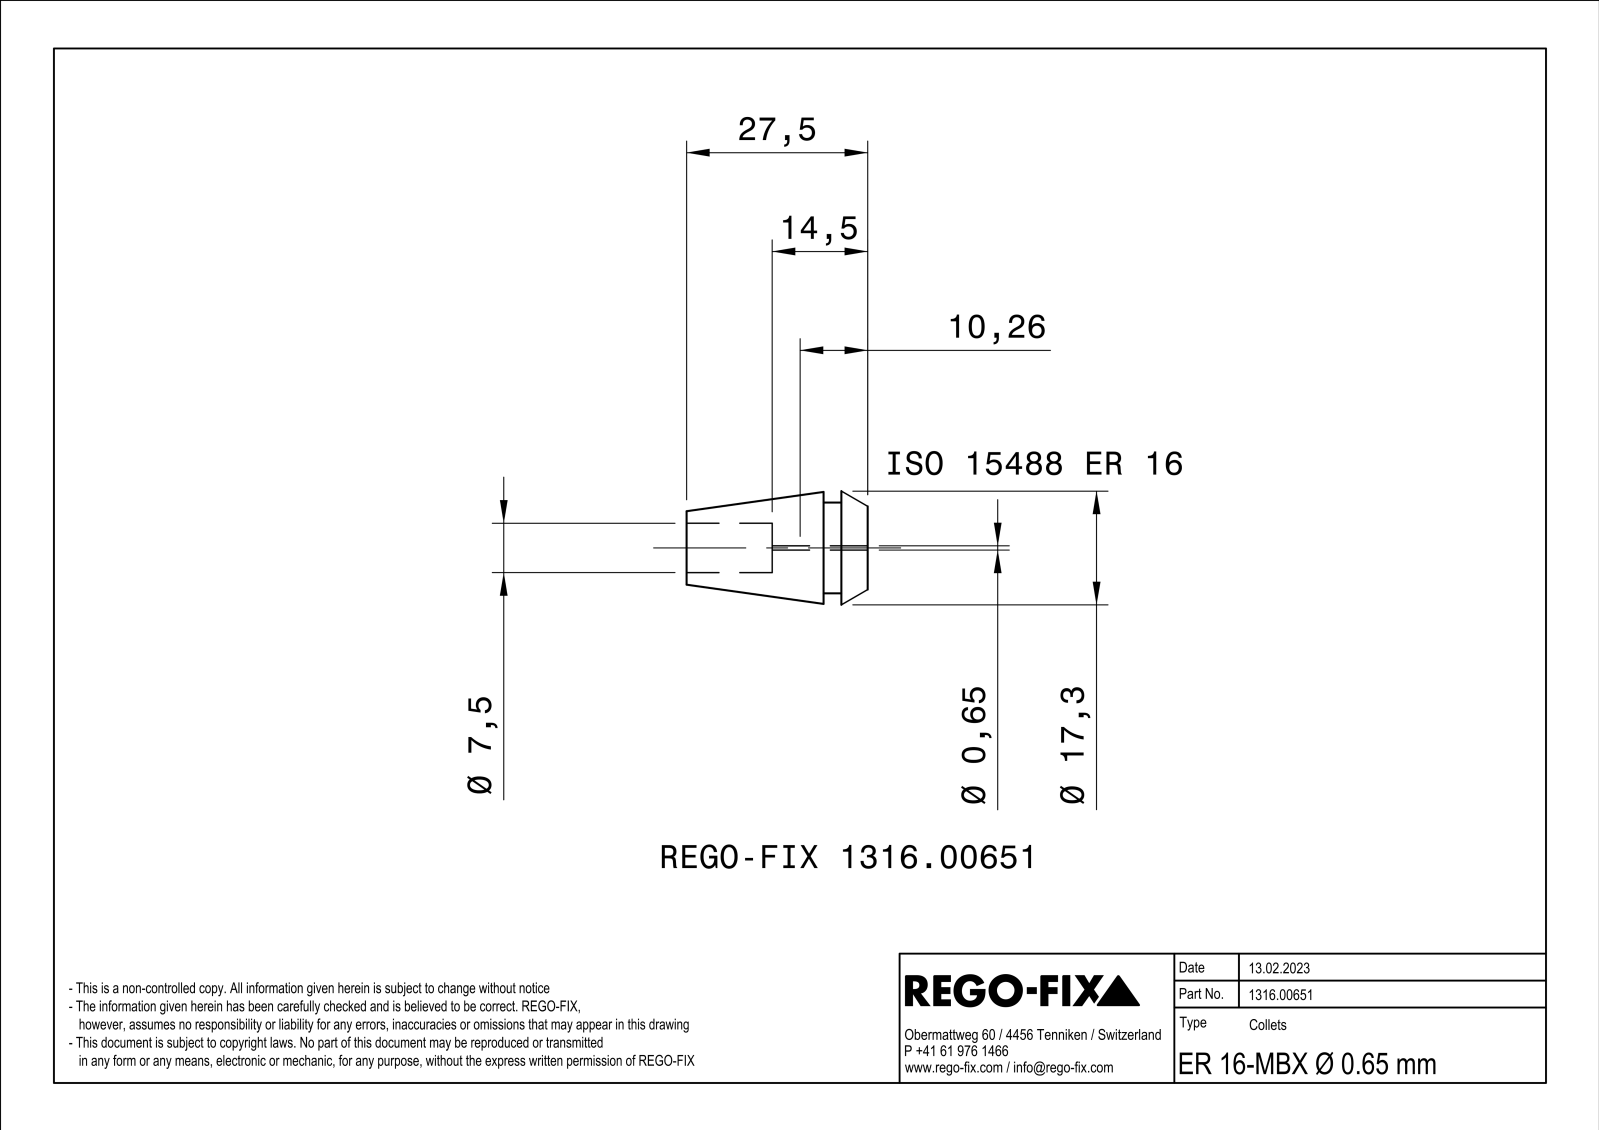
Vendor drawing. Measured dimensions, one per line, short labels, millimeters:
name: NOCUT
written by: SIEMENS PLM Software Solid Edge ST10 (AUTOMOTIVE_DESIGN)
unit: mm
bodies: 1 solid, 109 faces (36 planar, 27 cylindrical, 46 other)
size: 27.5 × 16.91 × 16.9
volume: 3 318 mm³; area: 3 326 mm²
holes: 3× ⌀2, 1× ⌀7.5
bosses: 1× ⌀13.8
rounds: 3× R0.11, 3× R25, 1× R0.33
face distances: 0.51, 0.8, 6.7, 4, 2.7, 27.5, 23.5, 20.8, 14.5, 10.5
hole spacings: 2.1, 3.64
